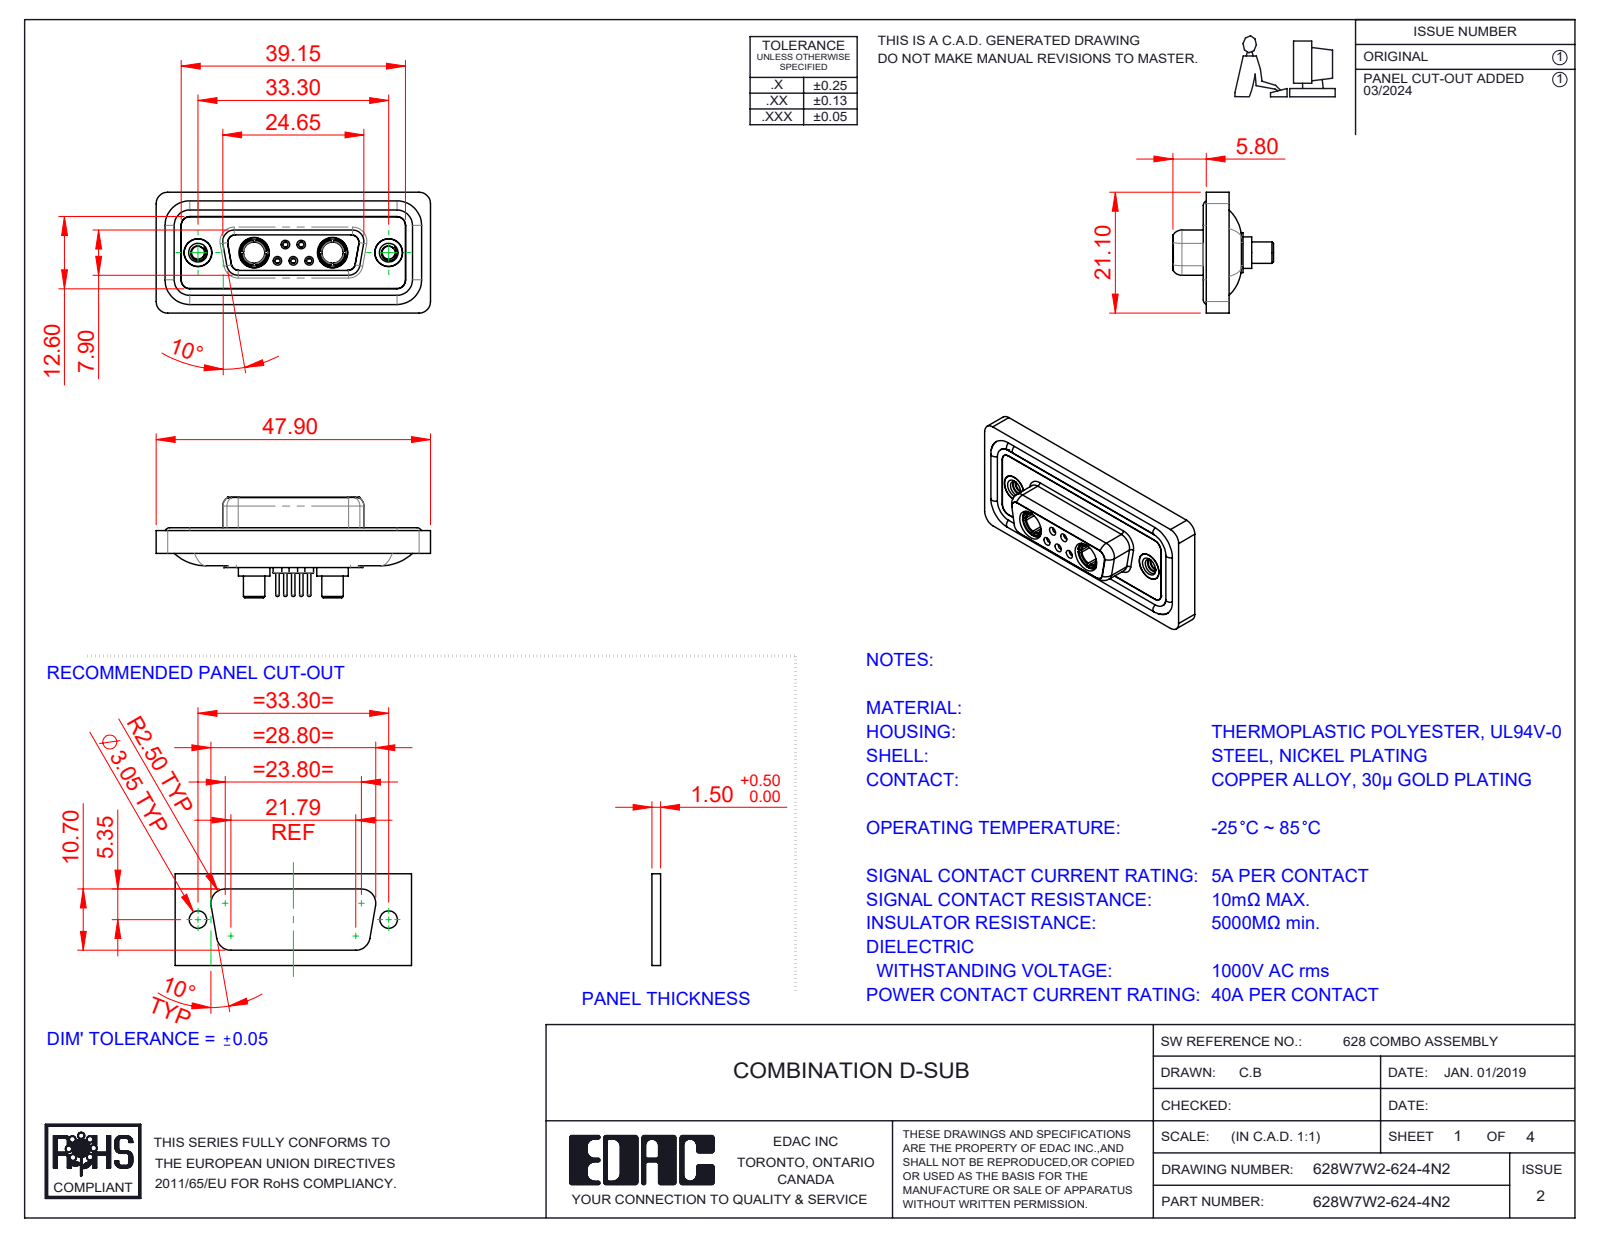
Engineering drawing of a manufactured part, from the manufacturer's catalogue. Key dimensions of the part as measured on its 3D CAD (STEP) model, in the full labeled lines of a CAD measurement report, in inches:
Part name (STEP PRODUCT): 628Combo Contact Row 2_24; 628Combo Shell Rear_15 Contacts; 628Combo Waterproof Housing_15 Contacts; 628W7W2-624-4N2 (+5 more)
STEP written by: SolidWorks 2023 (CONFIG_CONTROL_DESIGN)
Units: inches
Bodies: 16 solids, 809 faces (238 planar, 329 cylindrical, 242 other)
Overall size (bounding box): 1.886 × 0.831 × 0.691
Volume: 0.373 in³ · Surface area: 15.36 in²
Round holes (diameter × count): ⌀0.035 ×5, ⌀0.043 ×5, ⌀0.059 ×5, ⌀0.079 ×5, ⌀0.191 ×4, ⌀0.063 ×3, ⌀0.067 ×2, ⌀0.089 ×2, ⌀0.146 ×2, ⌀0.157 ×2, ⌀0.159 ×2, ⌀0.197 ×2
Round bosses / shafts (diameter × count): ⌀0.063 ×6, ⌀0.087 ×5, ⌀0.024 ×5, ⌀0.217 ×2, ⌀0.205 ×2, ⌀0.195 ×2, ⌀0.195 ×2, ⌀0.189 ×2
Partial cylindrical surfaces — rounded edges, fillets, slot ends (radius × count): R0.059 ×22, R0.079 ×20, R0.053 ×12, R0.063 ×8, R0.01 ×4, R0.02 ×4, R0.024 ×4, R0.026 ×4
Main face-to-face distances: 0.016, 0.071, 0.063, 0.02, 0.114, 0.293, 0.043, 0.222, 0.26, 0.278
Hole centre spacings: 0.124, 0.109, 0.386, 0.925, 0.17, 0.17, 0.198, 0.198
